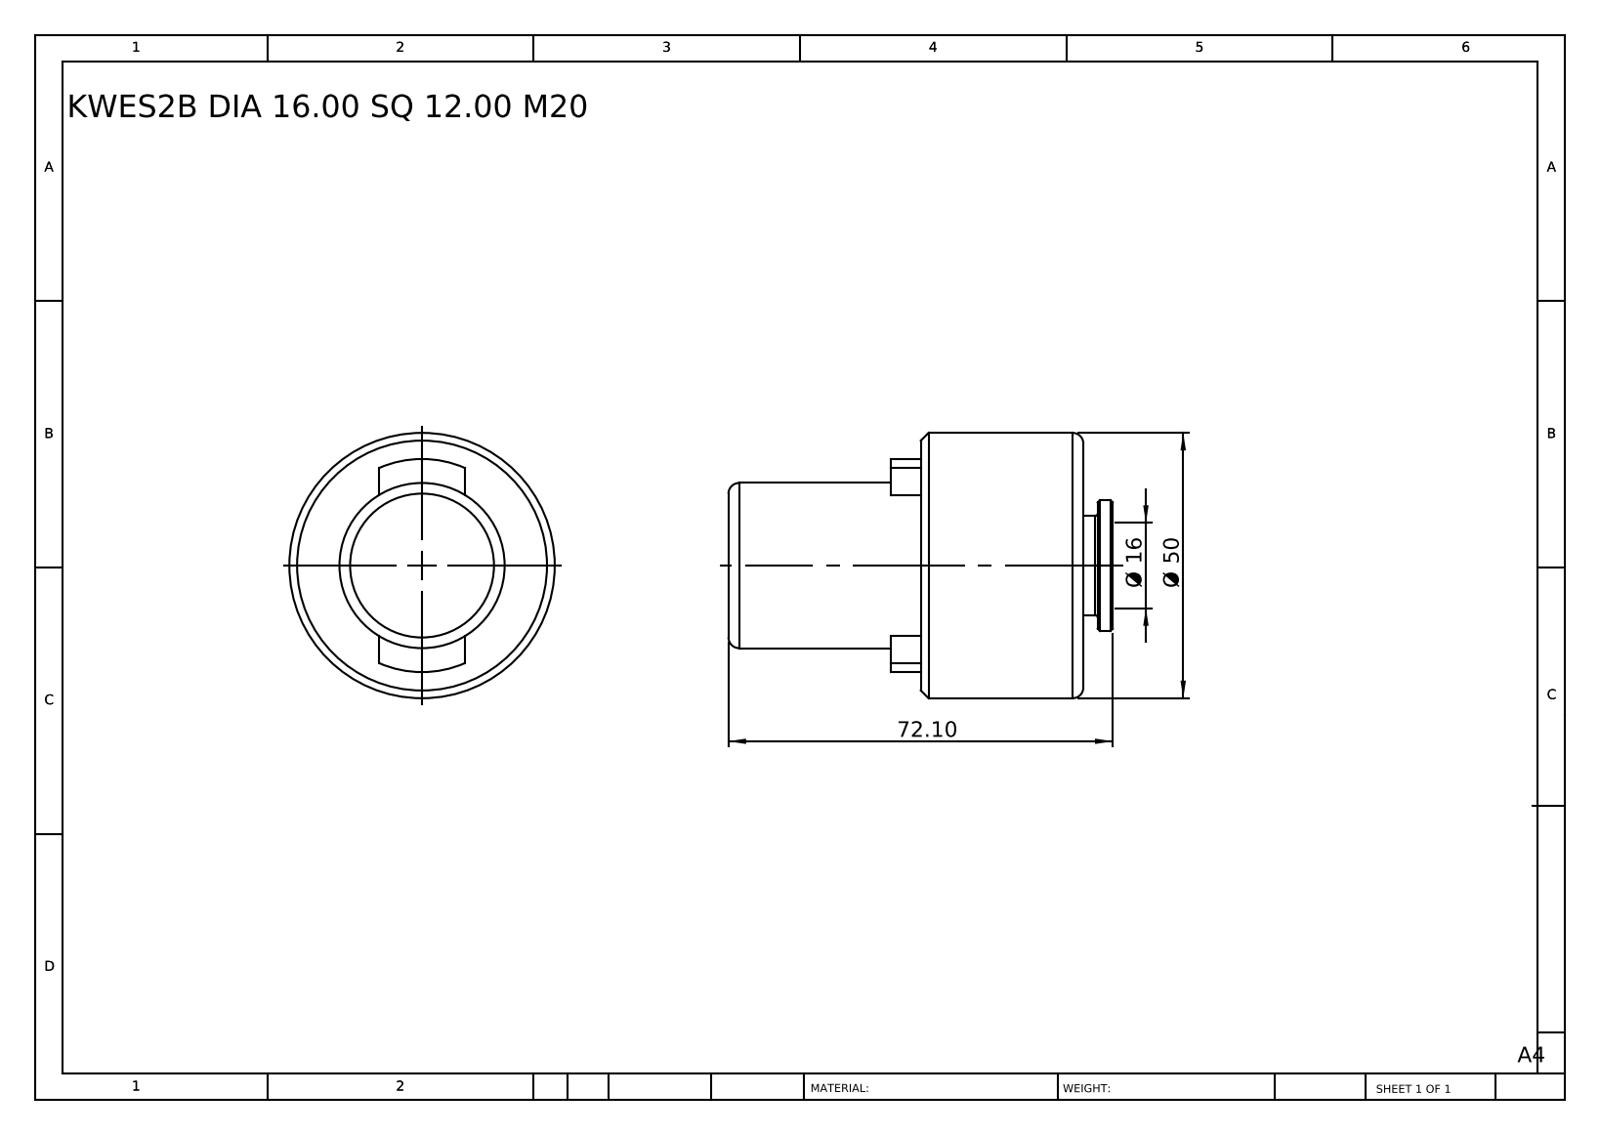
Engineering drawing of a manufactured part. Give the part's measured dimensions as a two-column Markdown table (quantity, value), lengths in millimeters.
| quantity | value |
| --- | --- |
| part name | KWES2B DIA 16.00 SQ 12.00 1-2'''''''' G(BSP) |
| STEP written by | SolidWorks 2014 (CONFIG_CONTROL_DESIGN) |
| units | millimeters |
| bodies | 1 solid, 38 faces (12 planar, 12 cylindrical, 14 other) |
| overall size | 72.1 × 49.8 × 49.8 |
| volume | 83 750 mm³ |
| surface area | 14 004 mm² |
| round holes (diameter × count) | 16 × 1 |
| round bosses / shafts (diameter × count) | 49.8 × 1, 31 × 1, 24.5 × 1, 18.6 × 1 |
| partial cylindrical surfaces (radius × count) | 20 × 1 |
| main face-to-face distances | 30.5, 36.1, 66.6, 72.1, 36, 5.5, 45.1, 9, 21.5, 27 |
